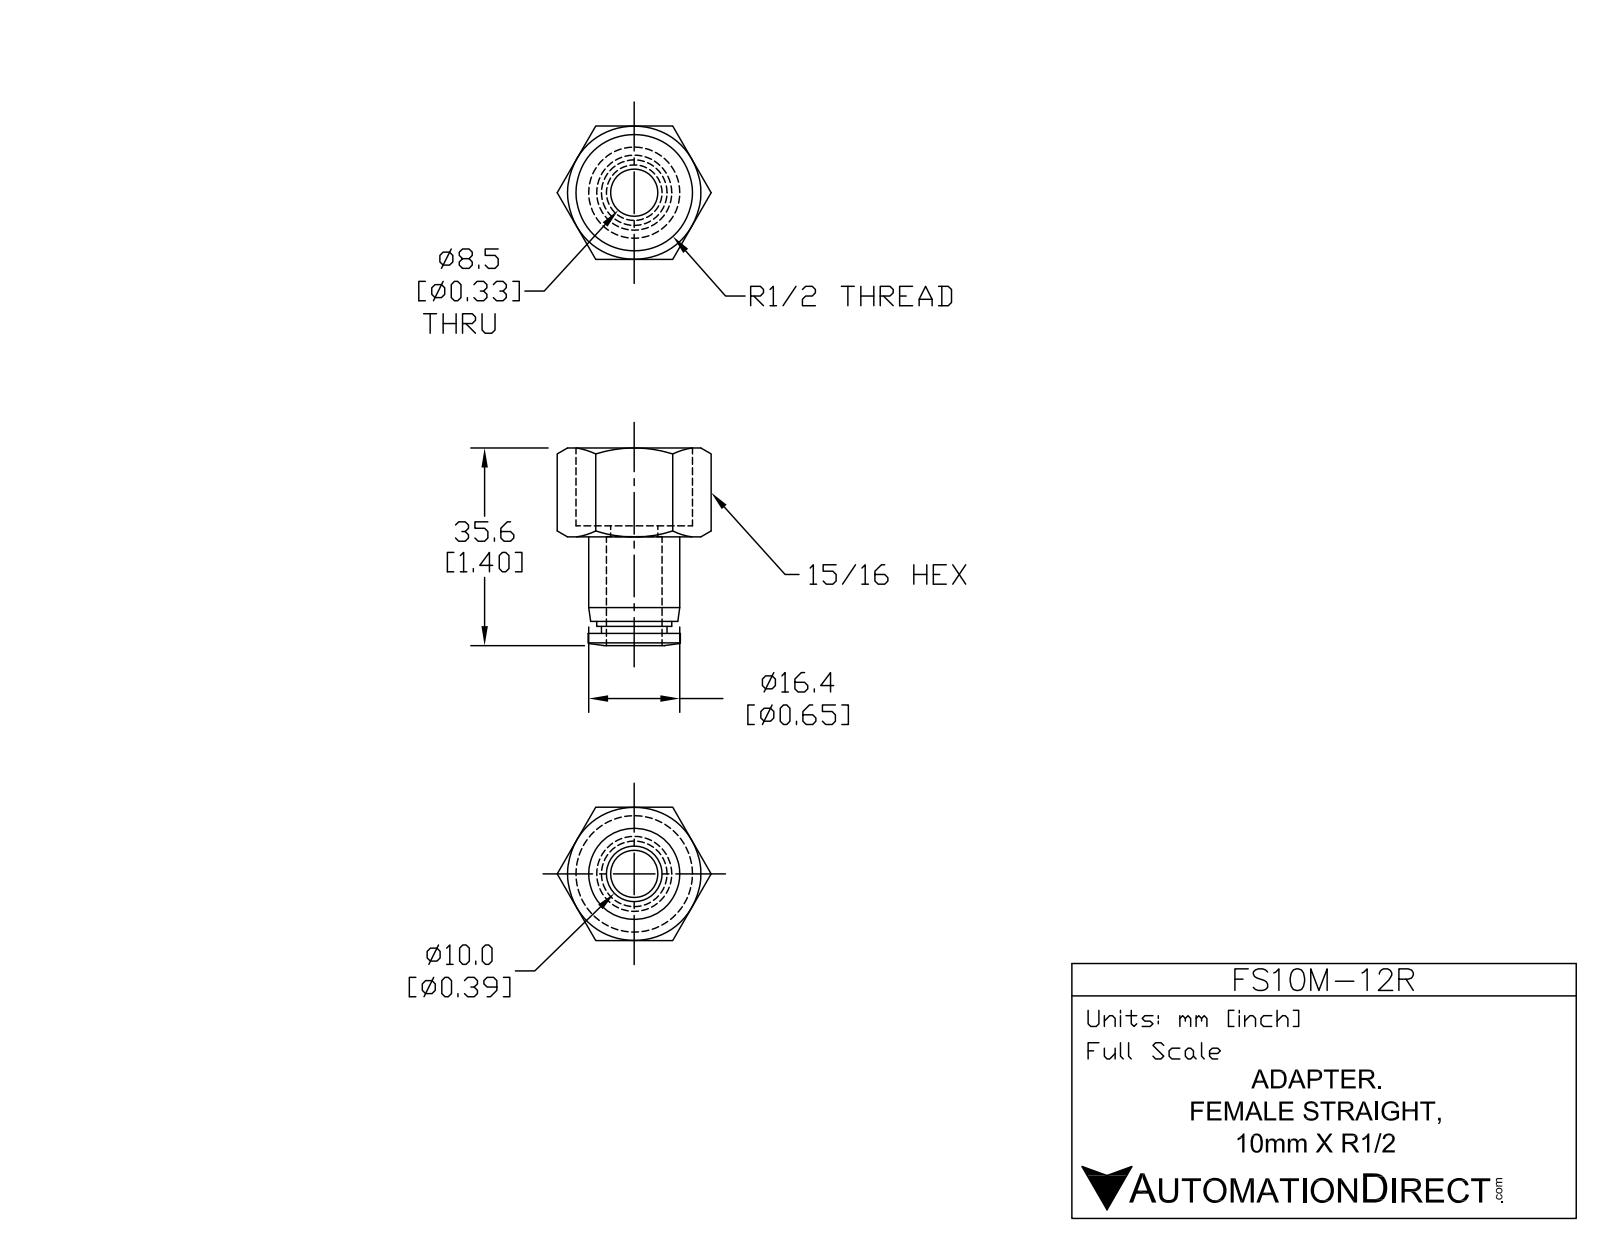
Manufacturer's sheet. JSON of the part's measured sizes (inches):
{"part_name": "FS10M-12R", "step_written_by": "SolidWorks 2015 (AUTOMOTIVE_DESIGN)", "units": "inches", "bodies": {"solids": 1, "faces": 50, "planar": 14, "cylindrical": 12, "other": 24}, "overall_size": [1.4, 1.091, 0.945], "volume_in3": 0.335, "surface_area_in2": 7.565, "round_holes": [[0.335, 1], [0.406, 1]], "round_bosses_or_shafts": [[0.654, 1], [0.646, 1], [0.531, 1], [0.465, 1]], "face_to_face_distances": [0.945, 0.079, 0.551, 0.63, 1.313, 0.762, 0.683, 1.228, 0.677, 0.598]}
